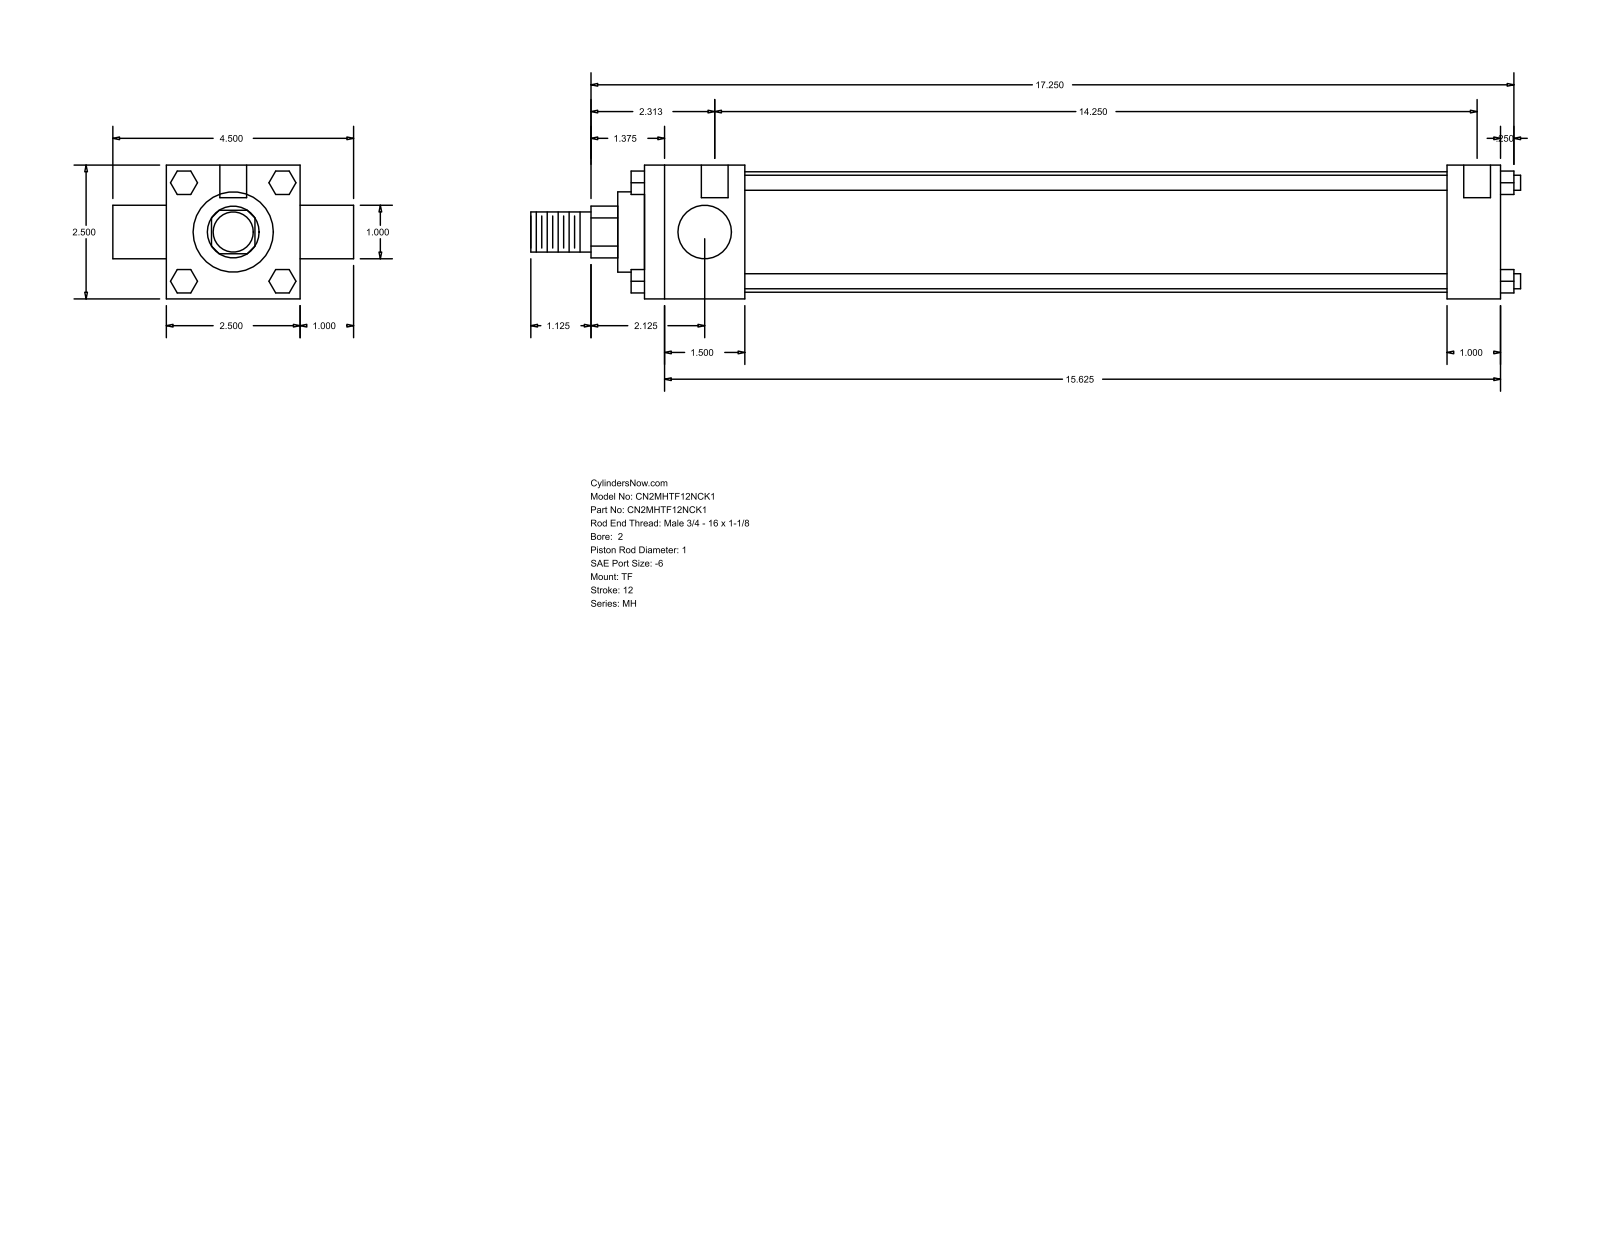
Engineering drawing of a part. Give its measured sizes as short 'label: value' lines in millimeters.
name: MH_TF__0200_1
written by: GSSL Pune (CONFIG_CONTROL_DESIGN)
unit: mm
bodies: 0 solids, 120 faces (92 planar, 28 cylindrical, 0 other)
size: 469.9 × 114.3 × 63.5
holes: 3× ⌀5.56, 2× ⌀12.7
bosses: 4× ⌀7.14, 2× ⌀25.4, 1× ⌀57.15, 1× ⌀38.1, 1× ⌀19.05
rounds: 1× R12.29
face distances: 63.5, 406.4, 25.4, 47.63, 381, 333.37, 358.77, 88.9, 419.1, 6.35
hole spacings: 3.17, 4.76, 361.95, 365.12, 366.71, 369.88
